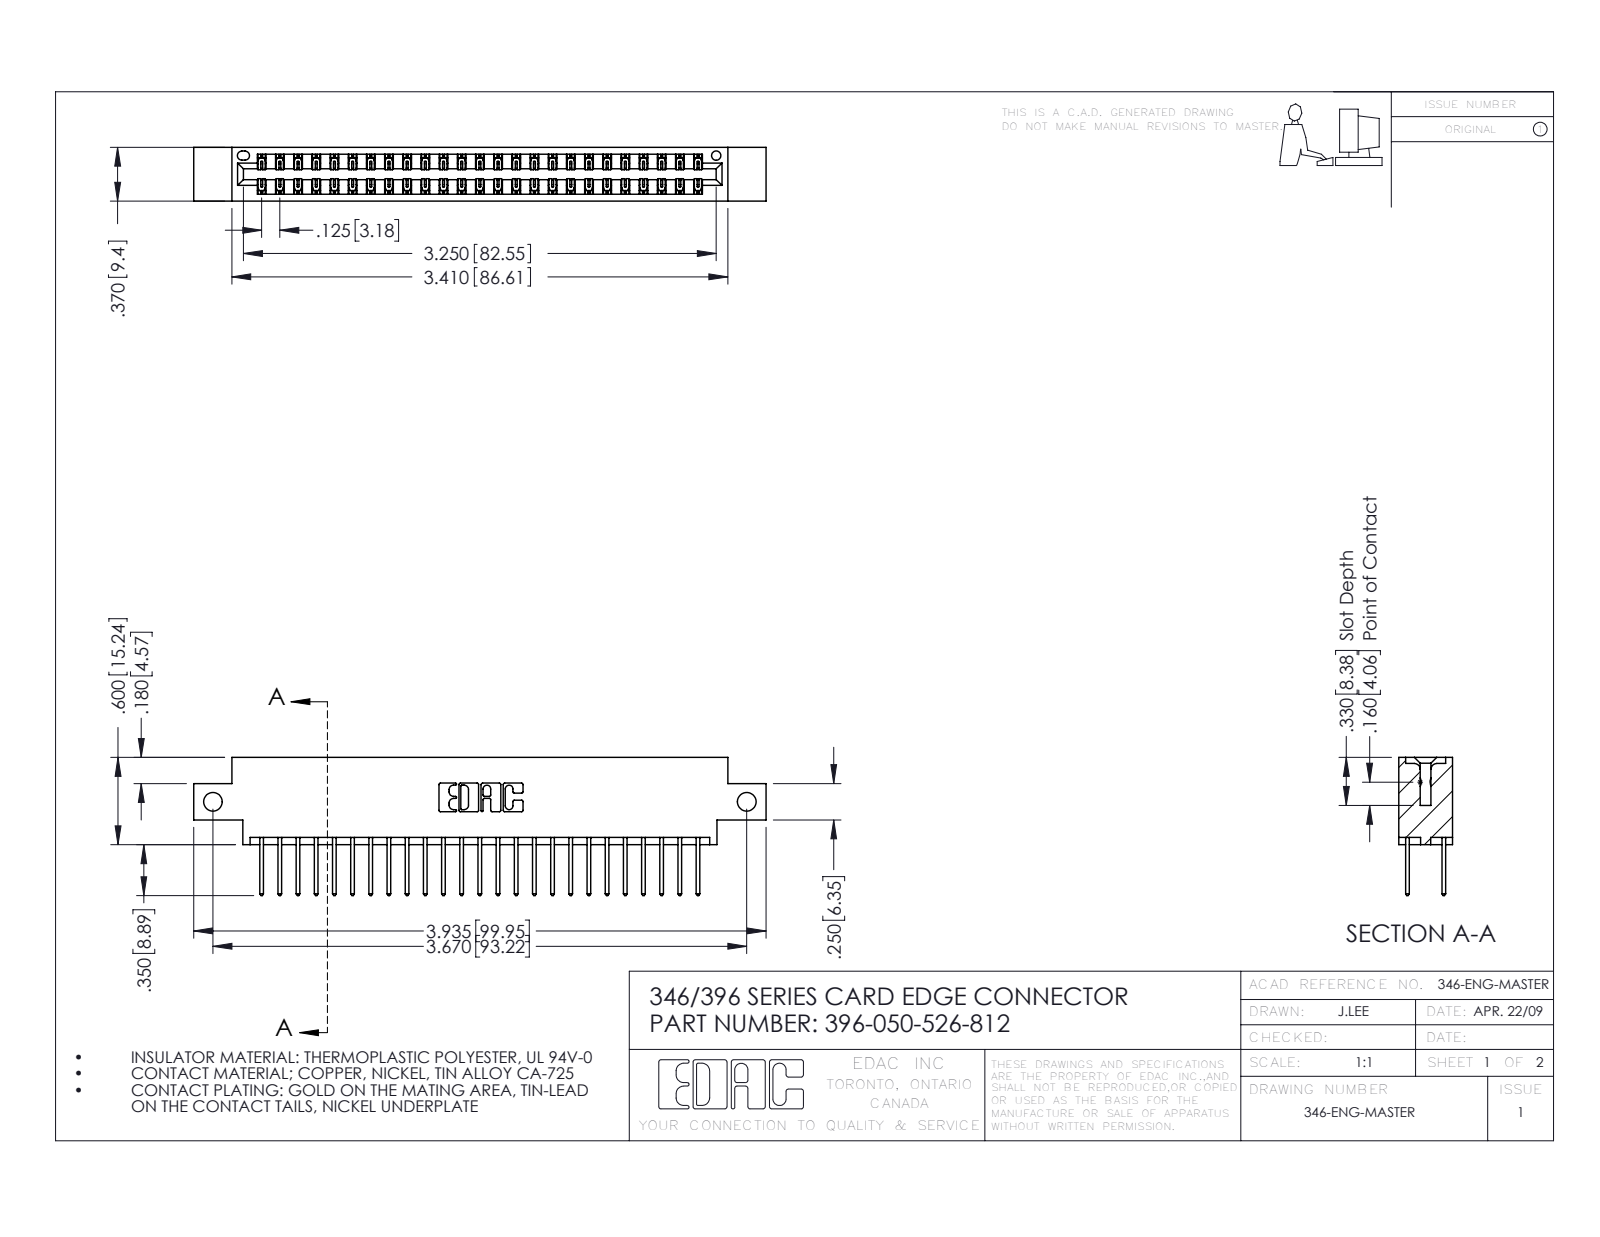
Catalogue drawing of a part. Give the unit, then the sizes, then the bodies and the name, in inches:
Units: inches
Overall size (bounding box): 3.935 × 0.95 × 0.37
Round holes (diameter × count): ⌀0.128 ×2, ⌀0.064 ×1
Partial cylindrical surfaces — rounded edges, fillets, slot ends (radius × count): R0.006 ×75, R0.01 ×50, R0.01 ×22, R0.007 ×6, R0.031 ×6, R0.026 ×3, R0.014 ×2, R0.022 ×2
Main face-to-face distances: 0.048, 0.322, 0.25, 0.37, 0.072, 0.298, 0.025, 0.275, 0.148, 0.222
Hole centre spacings: 3.67
Volume: 0.577 in³ · Surface area: 20.36 in²
Bodies: 51 solids, 2726 faces (1830 planar, 896 cylindrical, 0 other)
Part name (STEP PRODUCT): 345-292-001_345-293-126; 396-050-526-812; 346 Part_0.170 Offset - Side Mount
STEP written by: SolidWorks 2016 (CONFIG_CONTROL_DESIGN)
